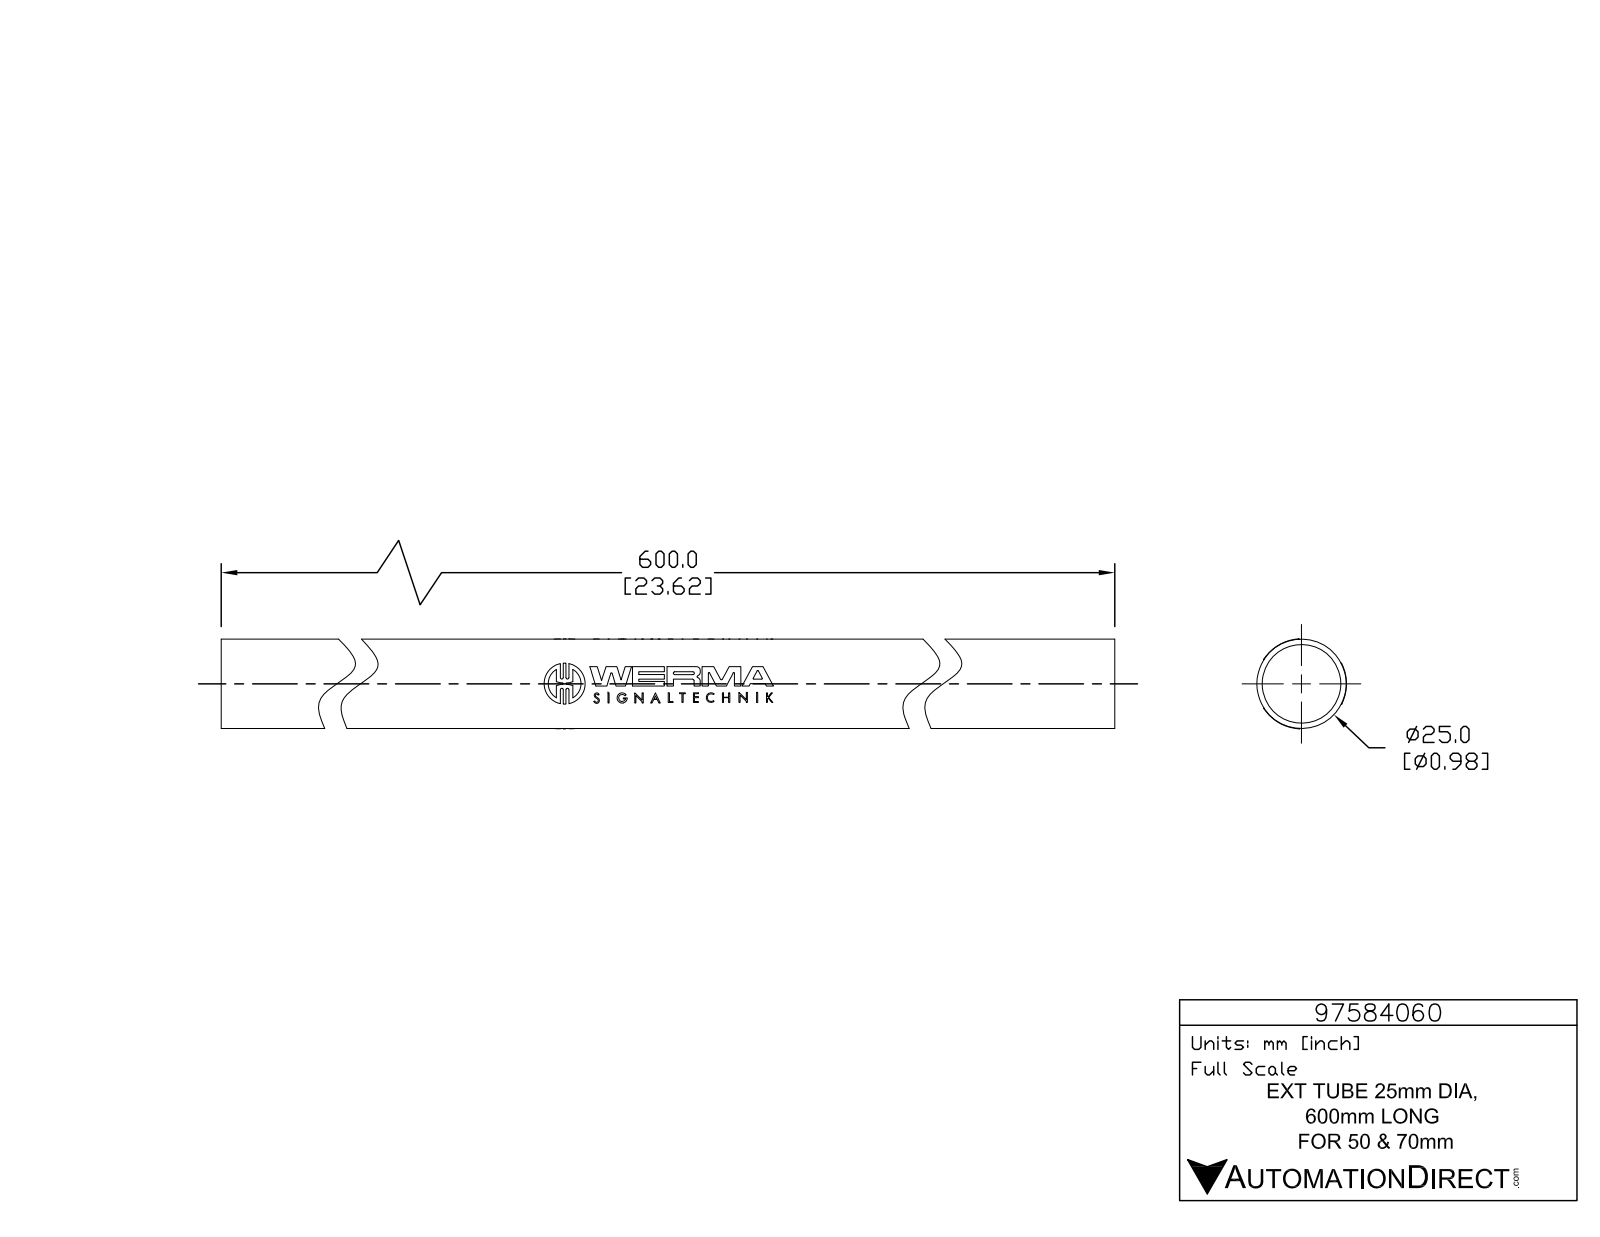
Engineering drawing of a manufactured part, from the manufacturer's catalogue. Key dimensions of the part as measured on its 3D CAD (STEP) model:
Part name (STEP PRODUCT): 97584060
STEP written by: SolidWorks 2015 (AUTOMOTIVE_DESIGN)
Units: inches
Bodies: 1 solid, 752 faces (521 planar, 231 cylindrical, 0 other)
Overall size (bounding box): 23.622 × 0.991 × 0.988
Volume: 4.06 in³ · Surface area: 137.9 in²
Round holes (diameter × count): ⌀0.078 ×3, ⌀0.866 ×1
Round bosses / shafts (diameter × count): ⌀0.452 ×3, ⌀0.113 ×3, ⌀0.984 ×1
Partial cylindrical surfaces — rounded edges, fillets, slot ends (radius × count): R0.007 ×9, R0.007 ×6, R0.016 ×6, R0.016 ×6, R0.016 ×6, R0.262 ×6, R0.006 ×3, R0.006 ×3
Main face-to-face distances: 23.622, 0.213, 0.075, 0.033, 0.061, 0.138, 0.05, 0.031, 0.182, 0.232
